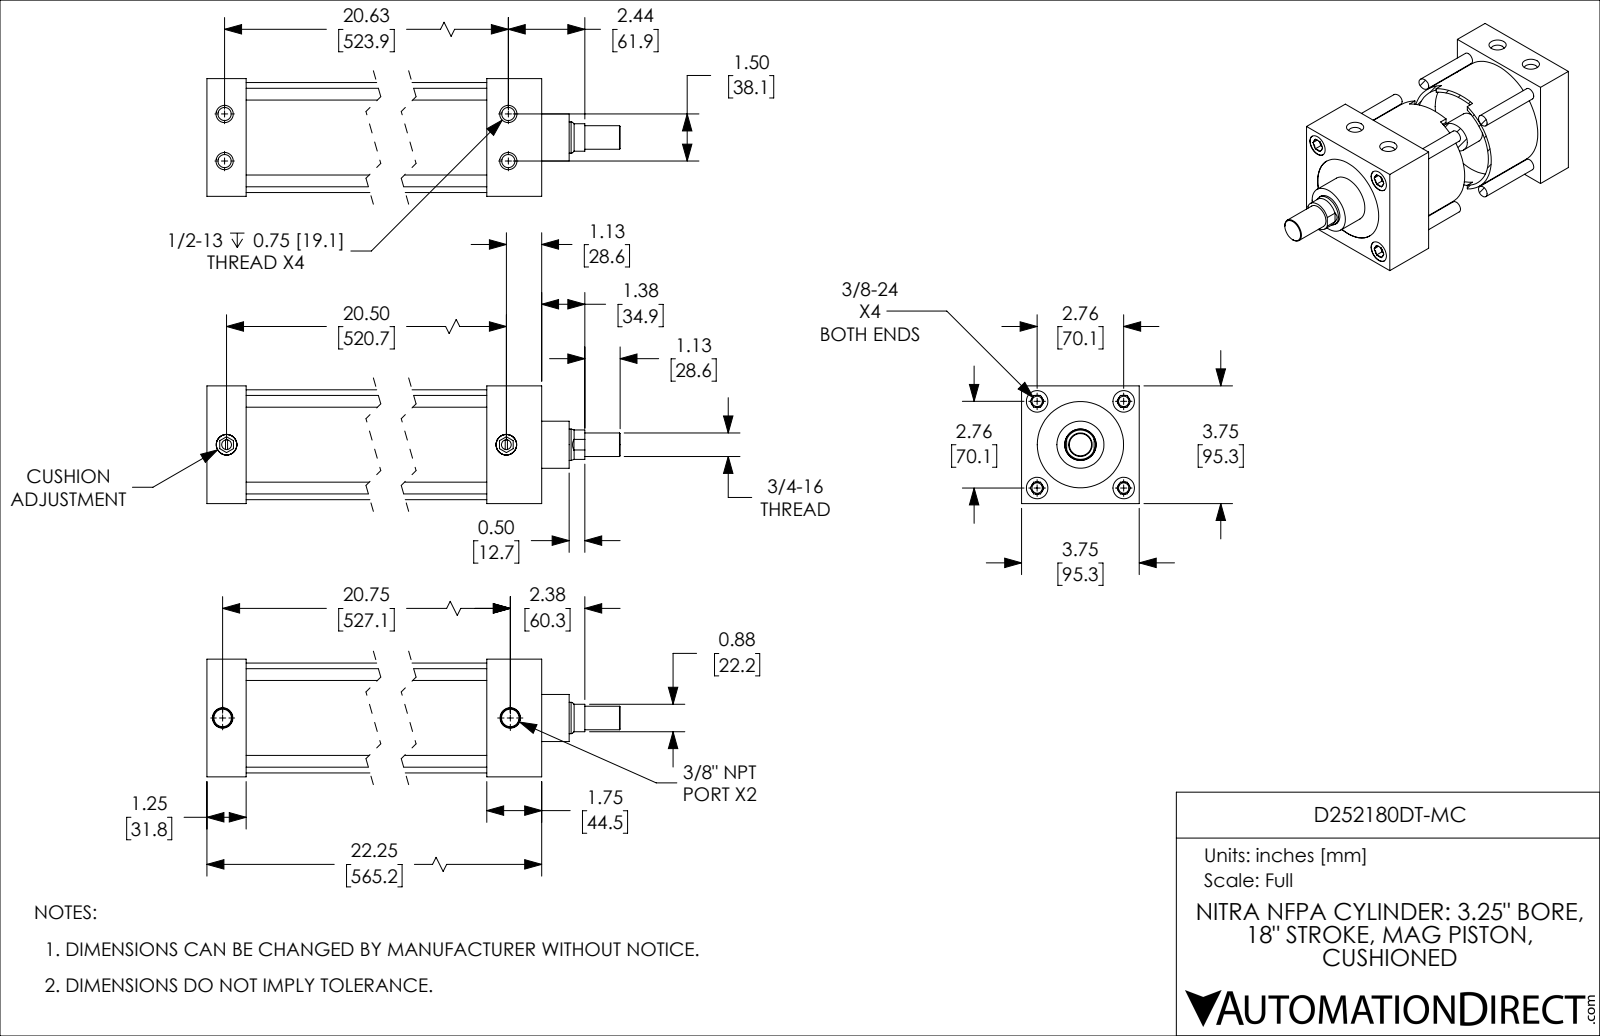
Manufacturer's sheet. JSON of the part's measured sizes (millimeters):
{"part_name": "D252180DT-MC; D252180DT-MC_PISTON_KK1; D252180DT-MC_CUSHION; D252180DT-MC_BODY", "step_written_by": "SolidWorks 2019 (CONFIG_CONTROL_DESIGN)", "units": "millimeters", "bodies": {"solids": 4, "faces": 246, "planar": 90, "cylindrical": 78, "other": 78}, "overall_size": [628.7, 95.3, 95.3], "volume_mm3": 1650000, "surface_area_mm2": 470300, "round_holes": [[8.4, 4], [10.7, 4], [17.4, 4], [7.9, 2], [14.3, 2], [16.7, 2], [25.4, 1], [69.9, 1], [82.6, 1]], "round_bosses_or_shafts": [[9.5, 4], [16.7, 2], [88.9, 1], [82.5, 1], [38.1, 1], [25.4, 1], [19.1, 1]], "partial_cylinders_radius": [[11.9, 1]], "face_to_face_distances": [31.8, 95.3, 520.7, 489, 63.5, 457.2, 565.2, 533.4, 501.7, 44.5], "hole_center_spacings": [19.1, 49.6, 70.1, 525.8, 38.1, 99.1, 523.9, 525.2]}
